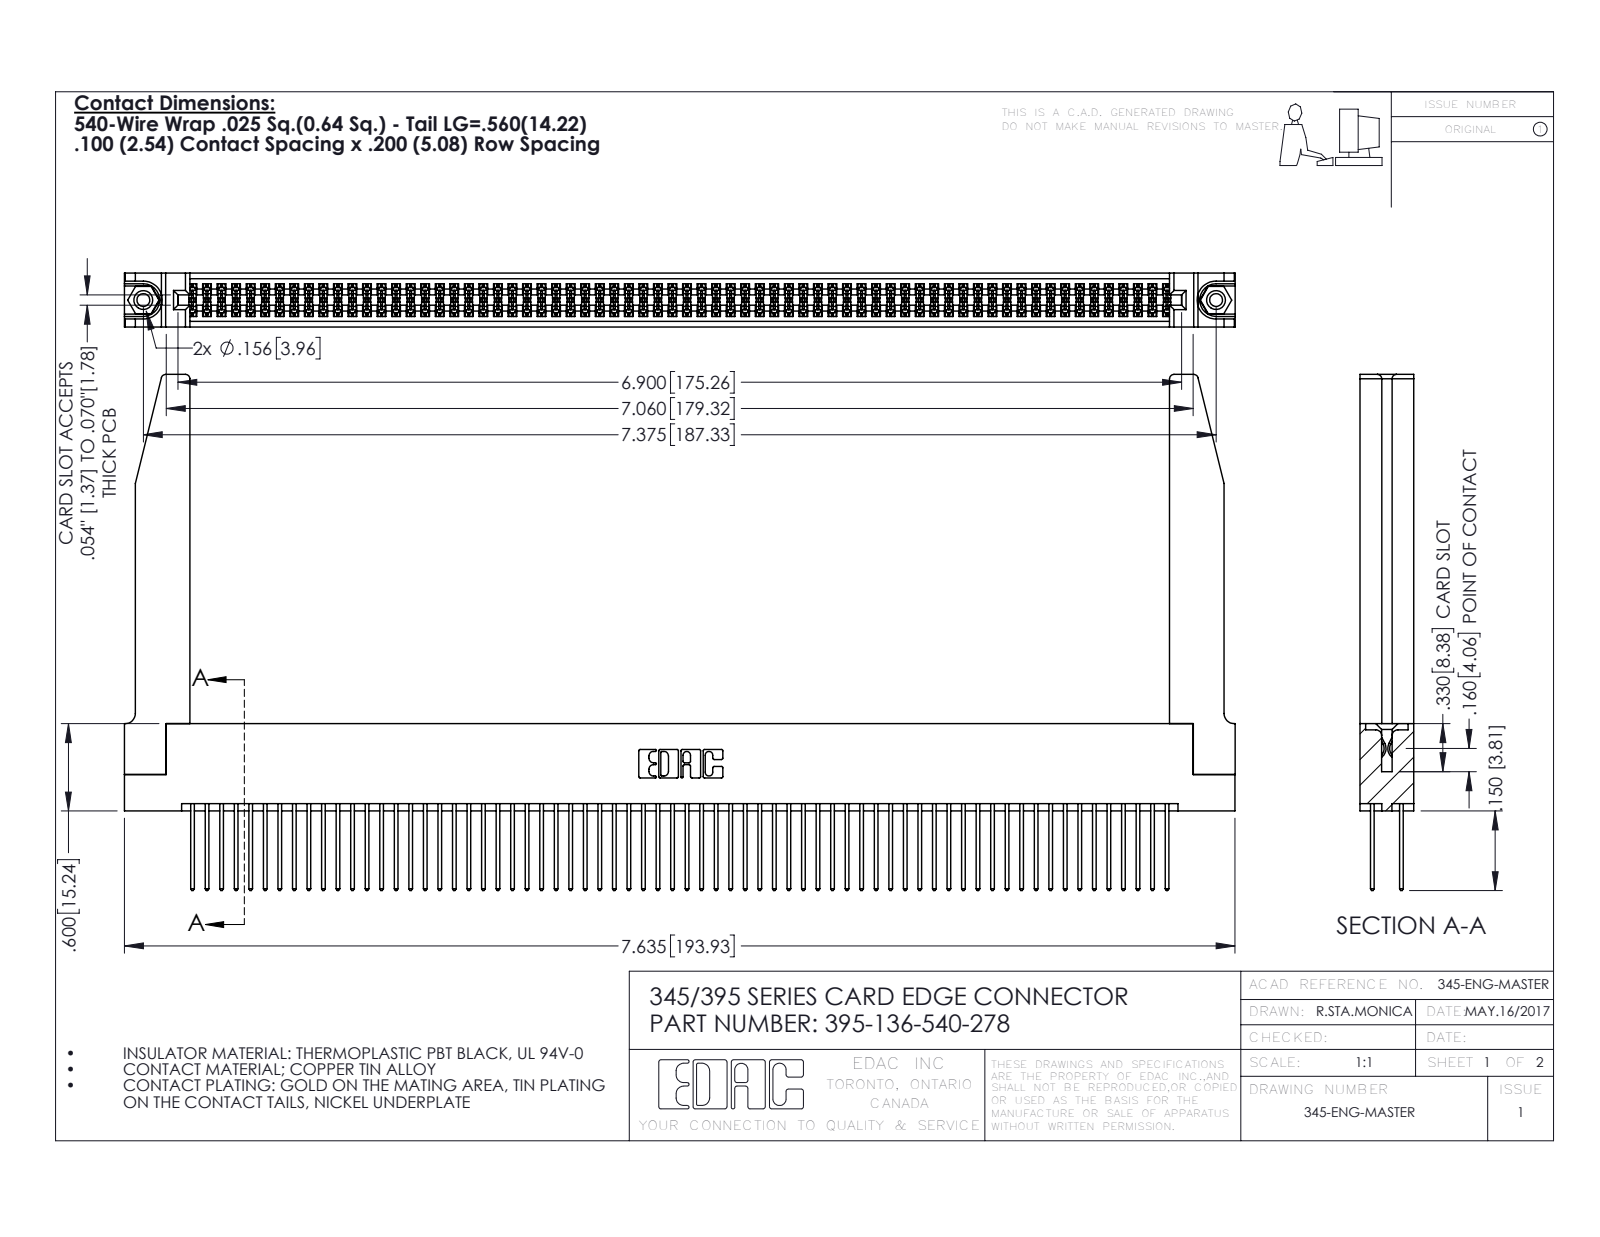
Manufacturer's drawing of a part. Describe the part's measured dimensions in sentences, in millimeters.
The part is named "345 Part_Flush Mounting Lugs - 0.156 Dia-TH; 345-292-001_345-293-140; 395-136-540-278; 345-250-001_345-250-001-102 (+1 more)". Its 3-D file was written by "SolidWorks 2016 (CONFIG_CONTROL_DESIGN)". It is 141 solids with 7160 faces: 4710 planar, 2398 cylindrical and 52 other. Overall it measures 194 by 90.1 by 9.4 millimeters. Its volume is 27 370 cubic millimeters and its surface area 38 700 square millimeters. Round holes: 2 of diameter 2.3, 2 of diameter 3.2, 2 of diameter 4, 1 of diameter 1.6. Round bosses or shafts: 2 of diameter 3.9. Partial cylindrical surfaces (rounded edges, fillets, slot ends): 204 of radius 0.2, 136 of radius 0.3, 22 of radius 0.3, 8 of radius 0.8, 6 of radius 0.2, 6 of radius 0.8, 3 of radius 0.7, 2 of radius 0.4. The main face-to-face distances are 1.8, 7.6, 9.4, 5.1, 2.5, 6.9, 0.6, 5.7, 4.4, 3.8. The hole center spacings are 6.9, 181.3, 187.3.
